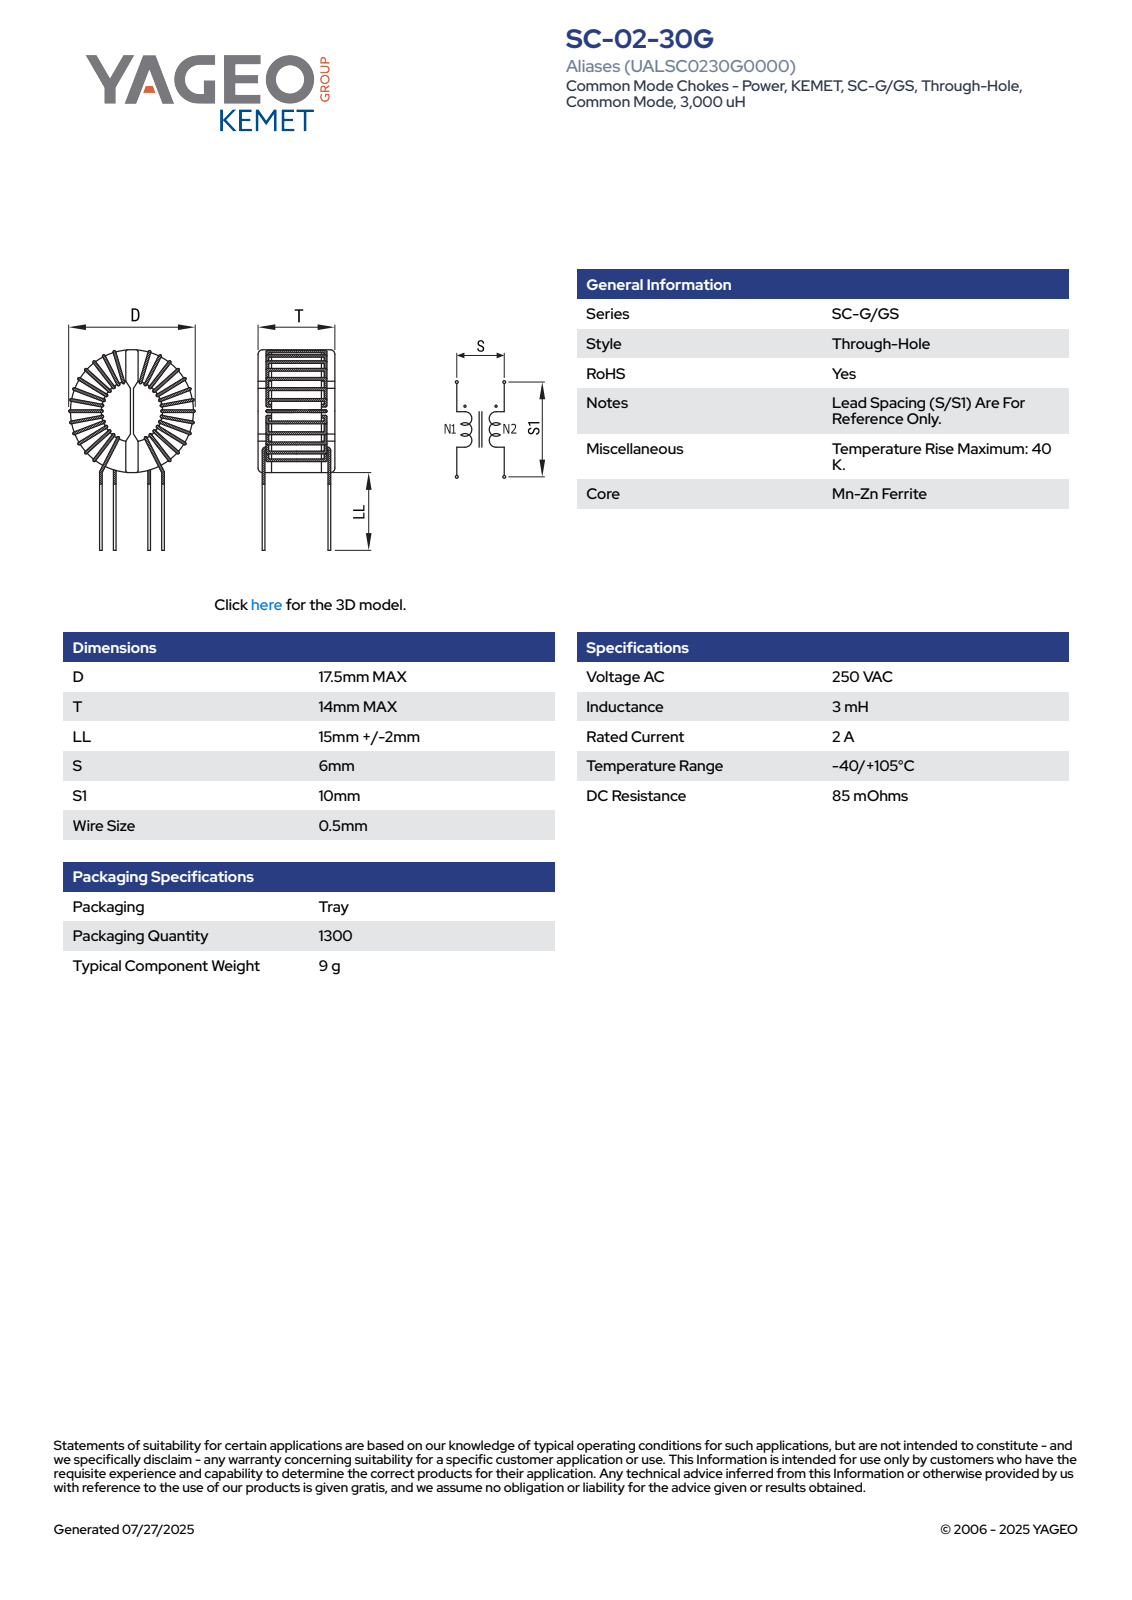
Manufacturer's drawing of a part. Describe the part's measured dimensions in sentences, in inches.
The part is named "SC-02-30G". Its 3-D file was written by "SolidWorks 2018 (AUTOMOTIVE_DESIGN)". It is 1 solid with 268 faces: 121 planar, 65 cylindrical and 82 other. Overall it measures 1.195 by 0.689 by 0.551 inches. Its volume is 0.109 cubic inches and its surface area 2.686 square inches. Round bosses or shafts: 8 of diameter 0.02. Partial cylindrical surfaces (rounded edges, fillets, slot ends): 16 of radius 0.01, 1 of radius 0.091, 1 of radius 0.126, 1 of radius 0.143, 1 of radius 0.144, 1 of radius 0.15, 1 of radius 0.25, 1 of radius 0.252. The main face-to-face distances are 0.047, 0.079, 0.327, 0.031, 0.126, 0.112, 0.439, 0.045, 0.081, 0.033.
